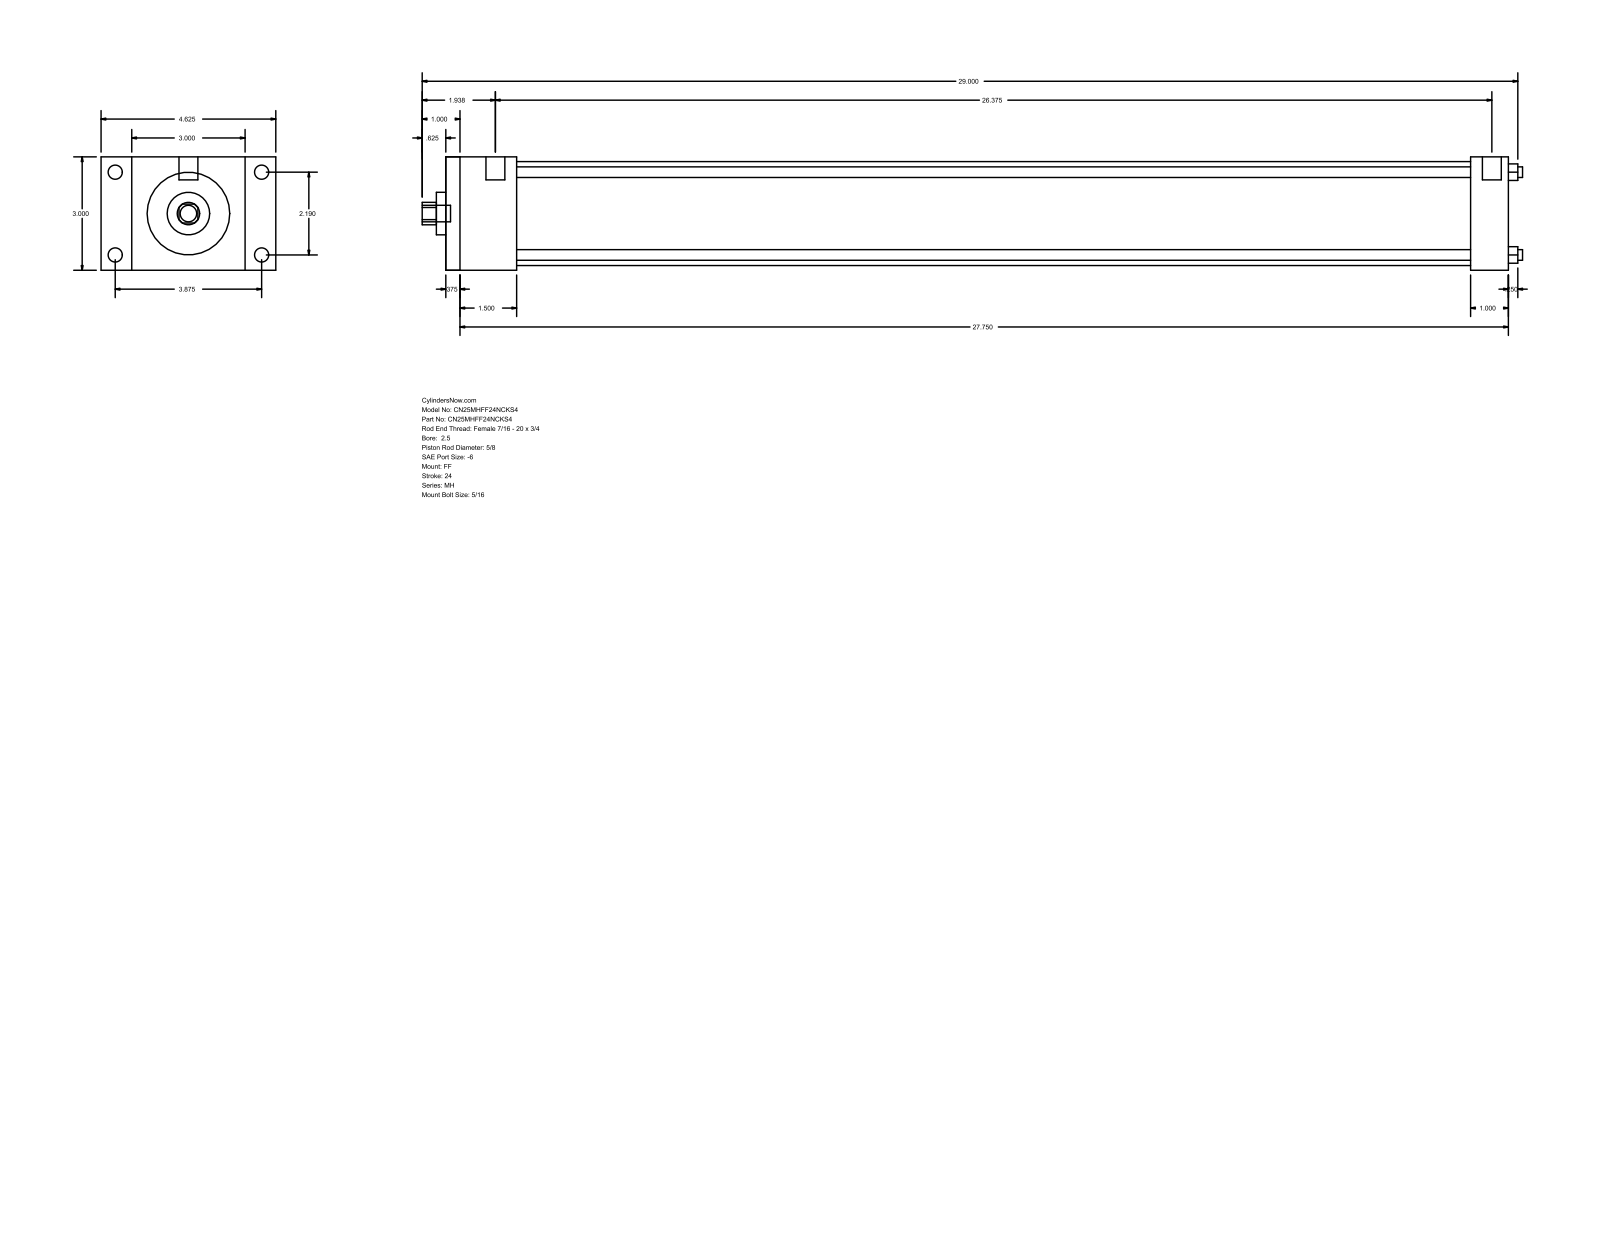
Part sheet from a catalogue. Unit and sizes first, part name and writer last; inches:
Units: inches
Overall size (bounding box): 29.125 × 4.625 × 3
Round holes (diameter × count): ⌀0.281 ×4, ⌀0.625 ×1, ⌀1.125 ×1, ⌀2.75 ×1
Round bosses / shafts (diameter × count): ⌀0.375 ×4, ⌀0.219 ×4, ⌀0.5 ×2, ⌀0.437 ×1
Partial cylindrical surfaces — rounded edges, fillets, slot ends (radius × count): R0.297 ×1
Main face-to-face distances: 3, 28.125, 0.375, 27.75, 1, 1.875, 27.125, 1.5, 26.75, 25.25
Hole centre spacings: 1.548, 2.19, 3.097
Bodies: 0 solids, 92 faces (64 planar, 28 cylindrical, 0 other)
Part name (STEP PRODUCT): MH_FF__0250_0.625
STEP written by: GSSL Pune (CONFIG_CONTROL_DESIGN)
